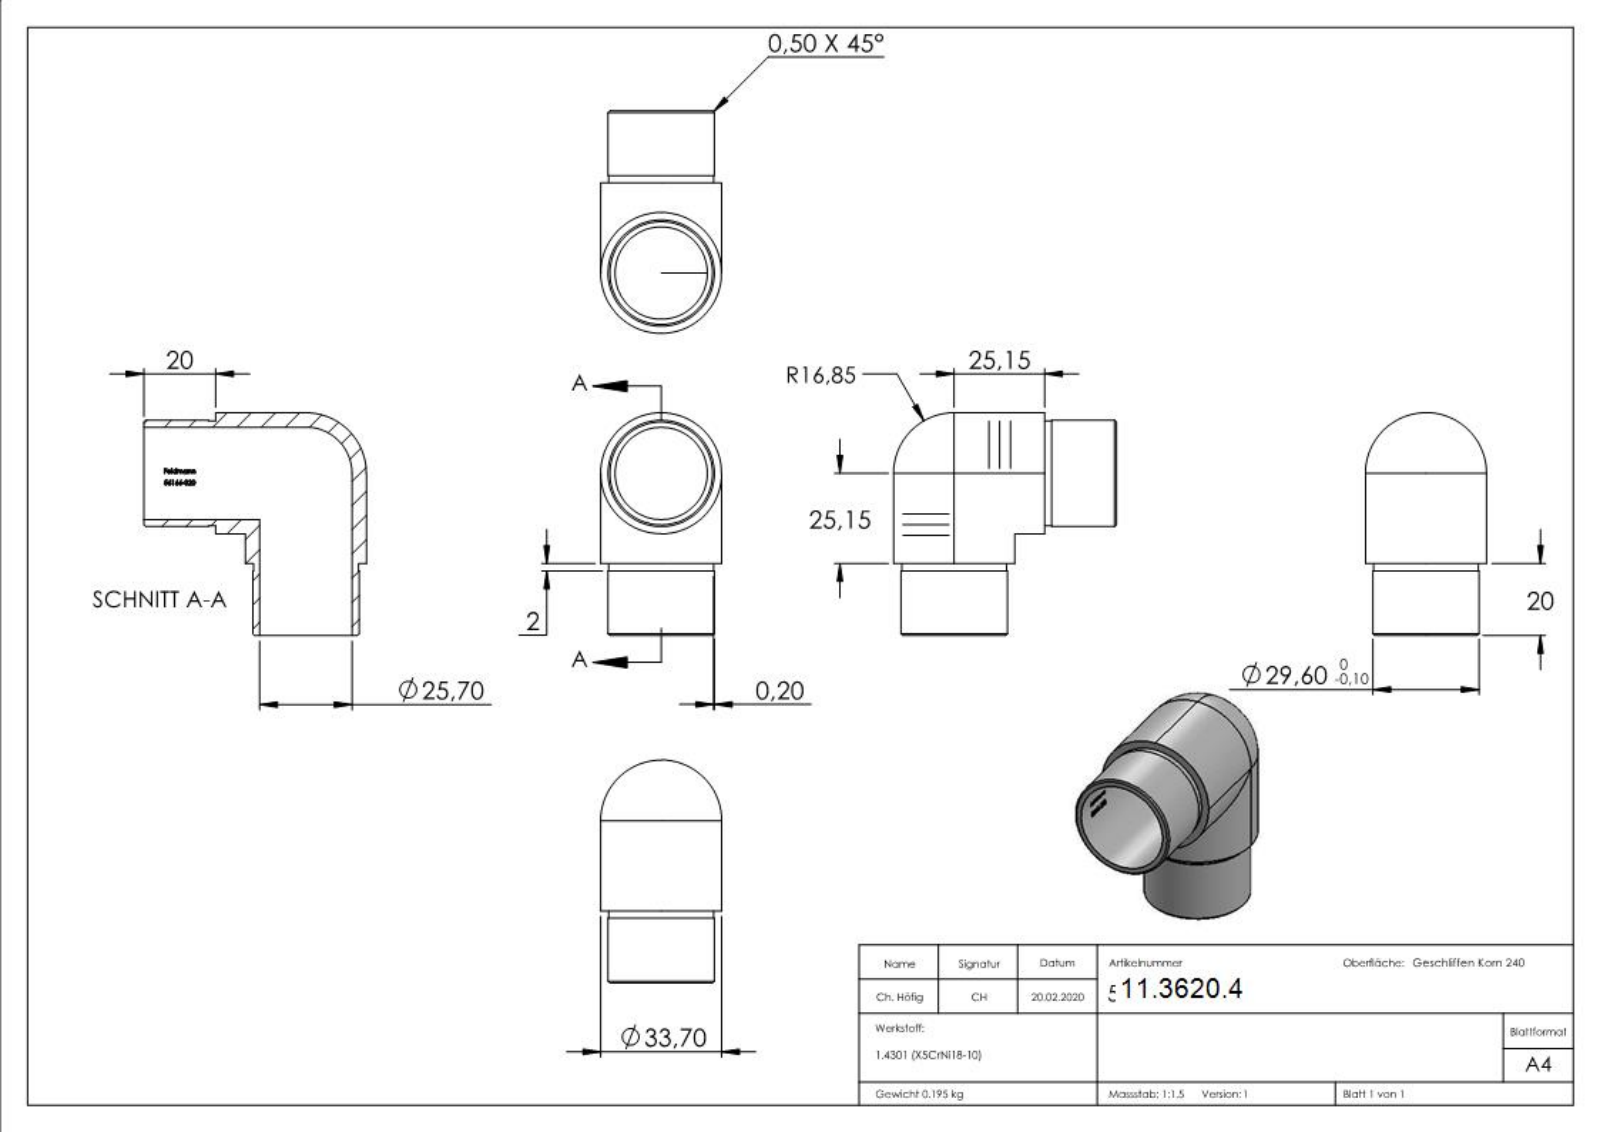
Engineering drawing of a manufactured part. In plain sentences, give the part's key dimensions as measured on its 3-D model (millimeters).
The part is named "56166-320". Its 3-D file was written by "SolidWorks 2015 (CONFIG_CONTROL_DESIGN)". It is 1 solid with 250 faces: 94 planar, 38 cylindrical and 118 other. Overall it measures 62 by 62 by 33.7 millimeters. Its volume is 24 687 cubic millimeters and its surface area 16 758 square millimeters. Round holes: 2 of diameter 25.7. Round bosses or shafts: 2 of diameter 33.7, 2 of diameter 29.6, 2 of diameter 29.2. Partial cylindrical surfaces (rounded edges, fillets, slot ends): 1 of radius 13.35. The main face-to-face distances are 20, 18, 2, 0.39, 1.26, 2.97, 4.23, 1.32, 3.66, 3.27.
